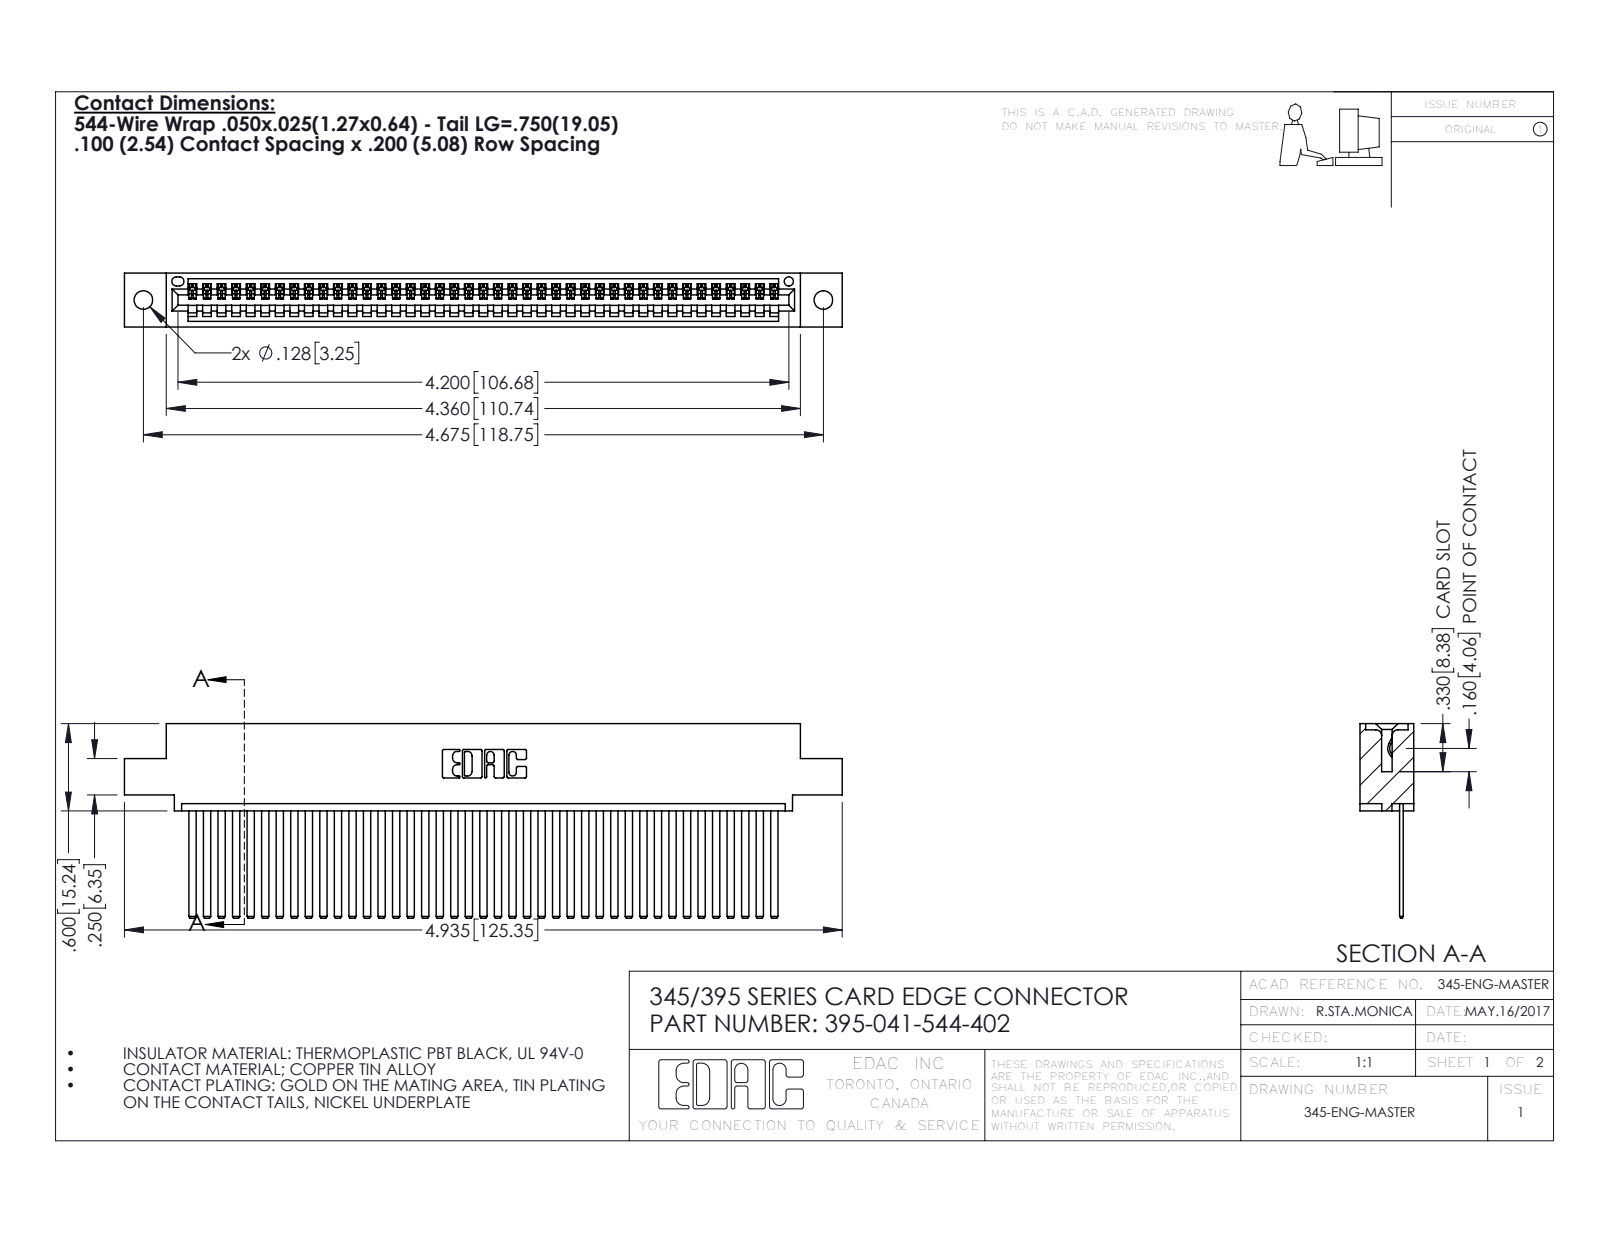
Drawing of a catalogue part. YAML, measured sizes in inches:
part_name: "345 Part_0.110 Offset - 0.128 Dia; 345-292-001_345-293-144; 395-041-544-402"
step_written_by: "SolidWorks 2016 (CONFIG_CONTROL_DESIGN)"
units: inches
bodies: {solids: 42, faces: 2262, planar: 1560, cylindrical: 702, other: 0}
overall_size: [4.935, 1.337, 0.37]
volume: 0.748
surface_area: 27.15
round_holes:
  - {diameter: 0.128, count: 2}
  - {diameter: 0.064, count: 1}
partial_cylinders:
  - {radius: 0.006, count: 82}
  - {radius: 0.01, count: 22}
  - {radius: 0.007, count: 6}
  - {radius: 0.031, count: 6}
  - {radius: 0.026, count: 3}
  - {radius: 0.031, count: 2}
  - {radius: 0.04, count: 2}
  - {radius: 0.014, count: 1}
face_to_face_distances: [0.072, 0.298, 0.025, 0.098, 0.272, 0.37, 0.2, 0.225, 0.149, 0.072]
hole_center_spacings: [0.27, 4.439, 4.675]
